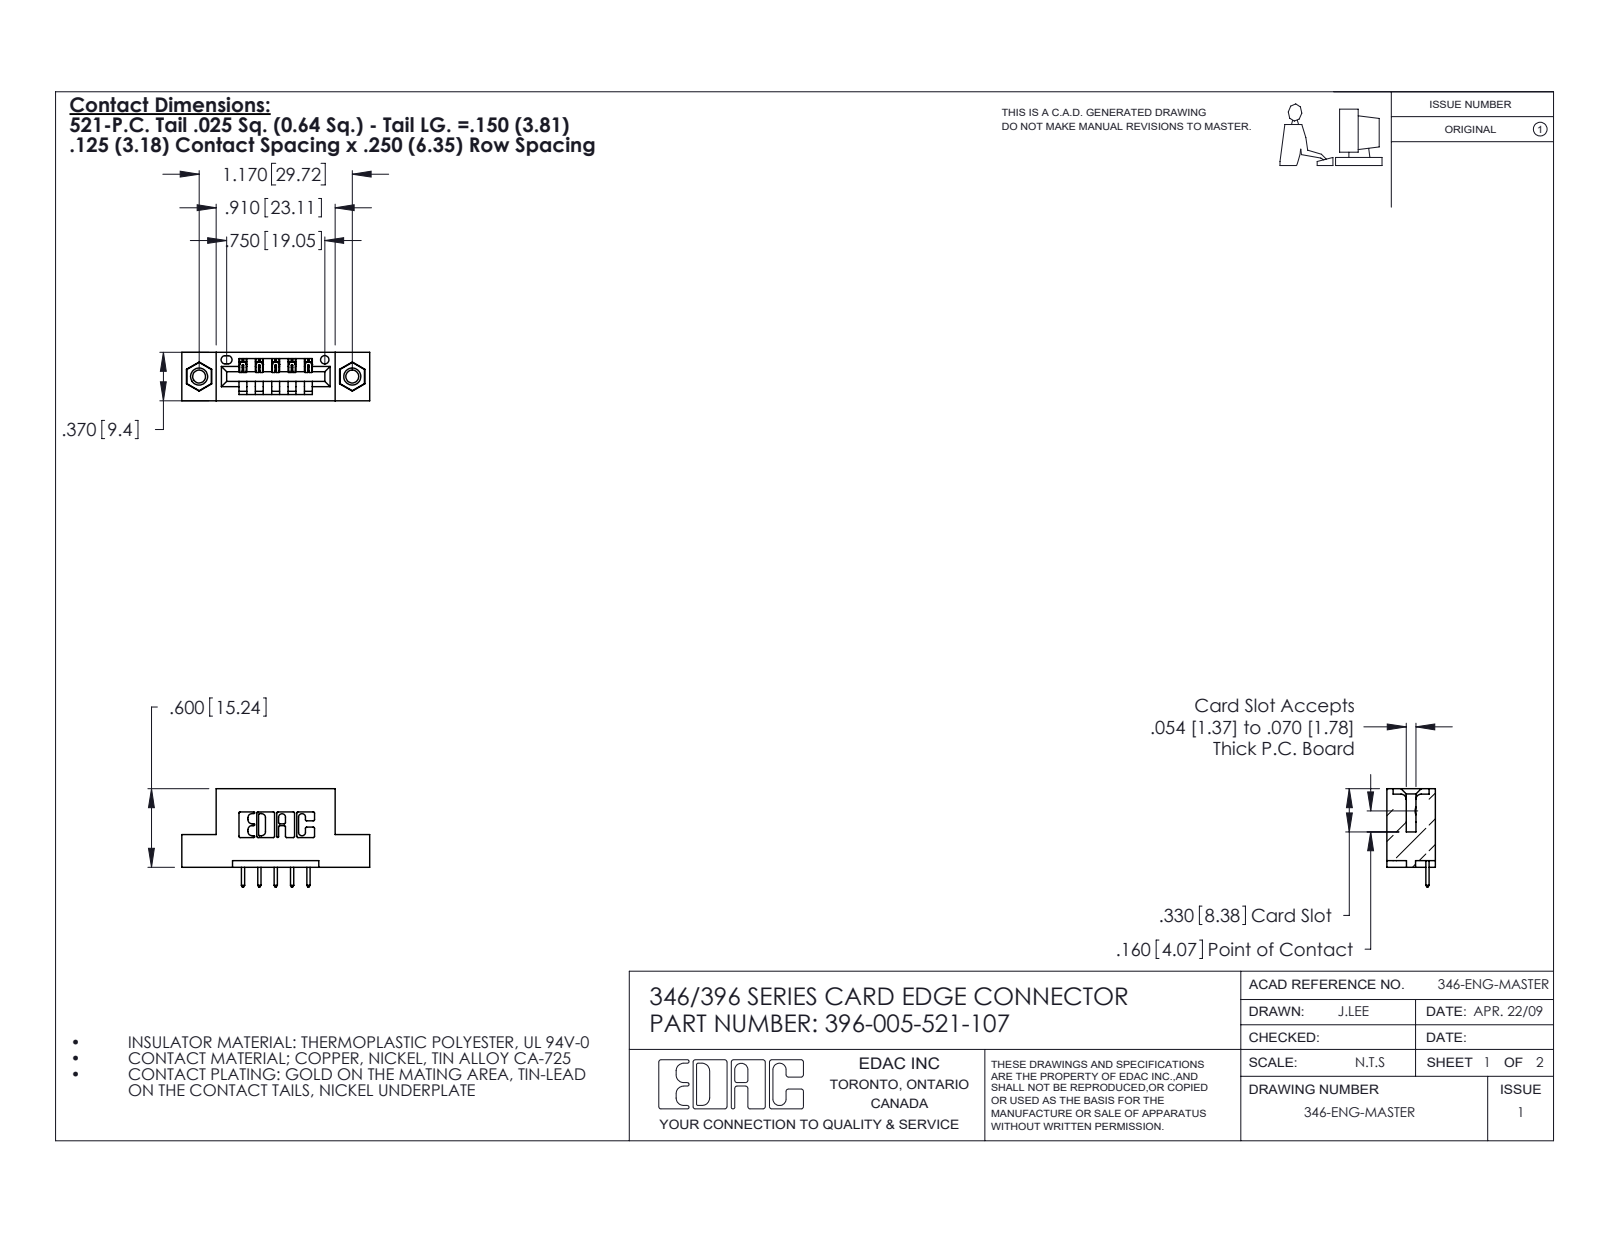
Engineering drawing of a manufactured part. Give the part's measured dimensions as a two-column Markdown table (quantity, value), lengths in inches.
| quantity | value |
| --- | --- |
| part name | 396-005-521-107; 345-292-001_345-293-121; 346 Part_Flush Mounting Lugs - 0.156 Dia-TI; 345-250-001_345-250-005-103 |
| STEP written by | SolidWorks 2020 (CONFIG_CONTROL_DESIGN) |
| units | inches |
| bodies | 8 solids, 472 faces (308 planar, 148 cylindrical, 16 other) |
| overall size | 1.435 × 0.75 × 0.37 |
| volume | 0.196 in³ |
| surface area | 5.559 in² |
| round holes (diameter × count) | 0.098 × 2, 0.125 × 2, 0.156 × 2, 0.064 × 1 |
| round bosses / shafts (diameter × count) | 0.155 × 2 |
| partial cylindrical surfaces (radius × count) | 0.01 × 22, 0.006 × 10, 0.01 × 10, 0.007 × 6, 0.031 × 6, 0.026 × 3, 0.031 × 2, 0.04 × 2 |
| main face-to-face distances | 0.25, 0.37, 0.048, 0.322, 0.55, 0.148, 0.222, 0.1, 0.174, 0.125 |
| hole center spacings | 0.246, 0.969, 1.17 |
